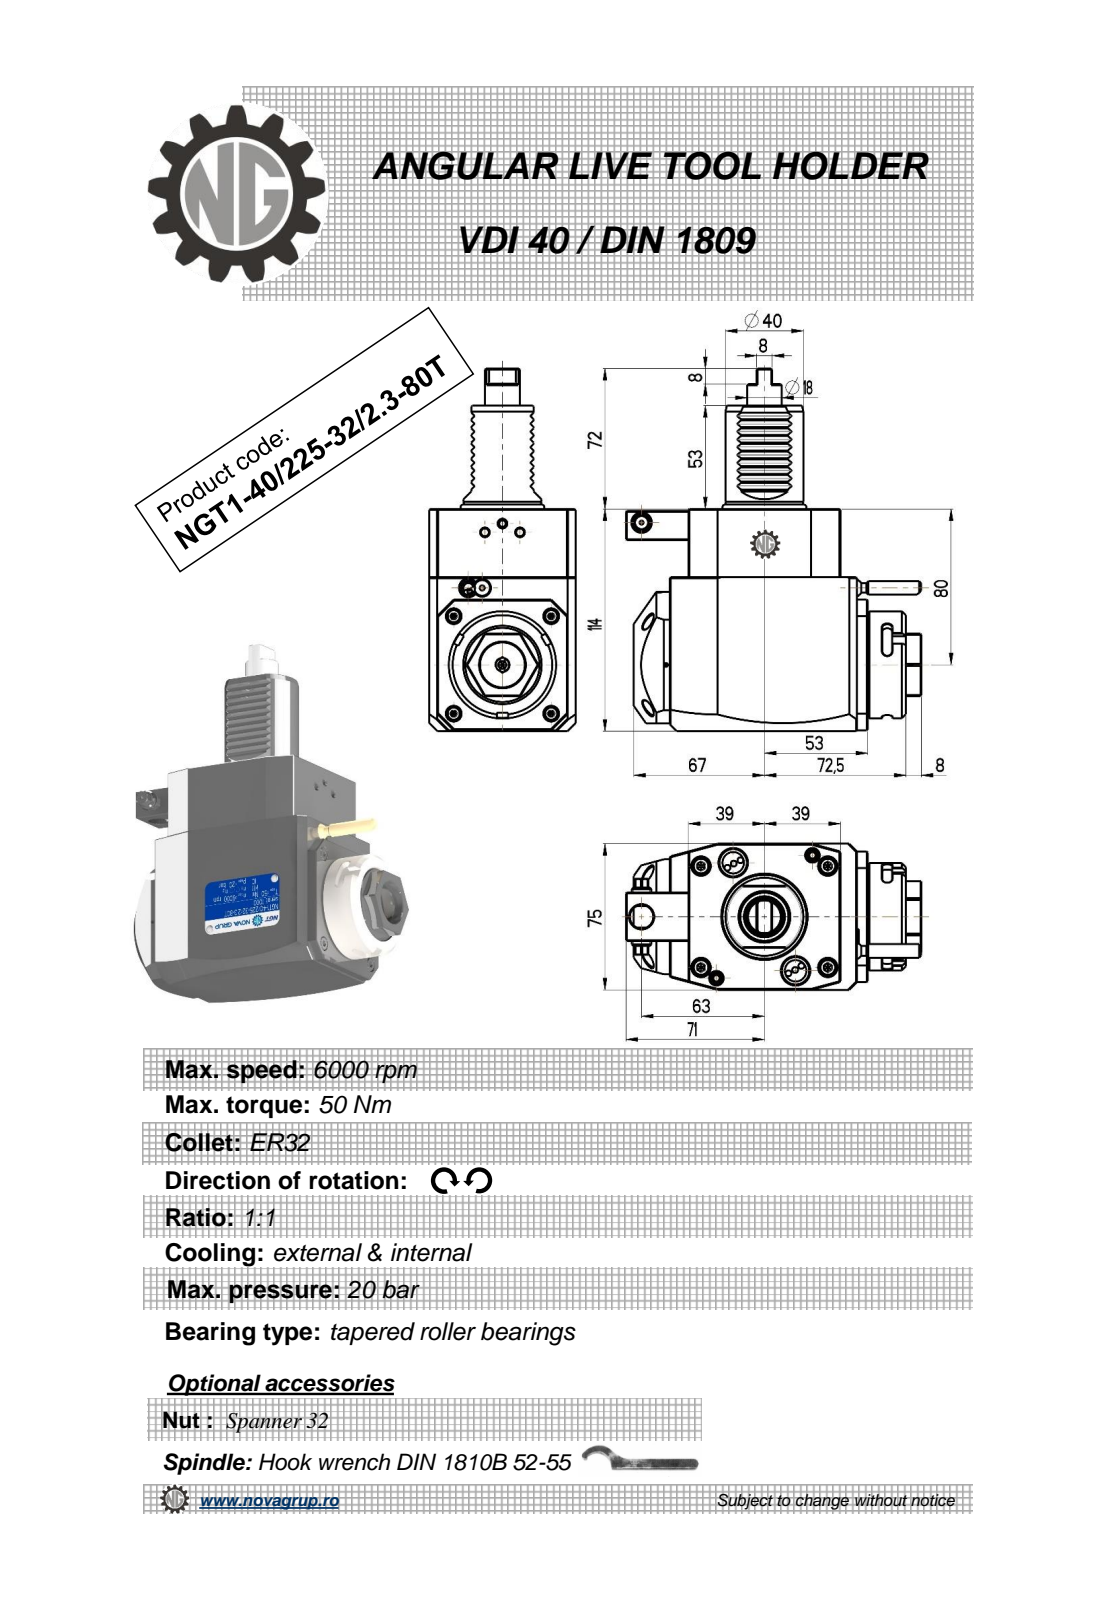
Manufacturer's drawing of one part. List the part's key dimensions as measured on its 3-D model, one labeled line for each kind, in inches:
Part name (STEP PRODUCT): NGT1_40_225_32_1_3_80T
STEP written by: PRO/ENGINEER BY PARAMETRIC TECHNOLOGY CORPORATION, 2010280 (CONFIG_CONTROL_DESIGN)
Units: inches
Bodies: 1 solid, 399 faces (228 planar, 93 cylindrical, 78 other)
Overall size (bounding box): 7.323 × 5.965 × 2.953
Volume: 58.05 in³ · Surface area: 111.2 in²
Round holes (diameter × count): ⌀0.079 ×1, ⌀0.098 ×1, ⌀0.118 ×1, ⌀0.177 ×1, ⌀0.374 ×1, ⌀0.472 ×1, ⌀0.906 ×1
Round bosses / shafts (diameter × count): ⌀0.315 ×2, ⌀2.165 ×1, ⌀1.89 ×1, ⌀1.575 ×1, ⌀0.701 ×1, ⌀0.394 ×1, ⌀0.276 ×1, ⌀0.197 ×1
Partial cylindrical surfaces — rounded edges, fillets, slot ends (radius × count): R0.012 ×20, R0.098 ×6, R0.031 ×2, R7.087 ×2, R0.152 ×1, R0.167 ×1, R0.965 ×1, R1.476 ×1
Main face-to-face distances: 2.953, 4.488, 0.551, 3.071, 3.622, 0.984, 4.39, 1.319, 0.768, 1.378
Hole centre spacings: 1.47, 1.701, 2.854
